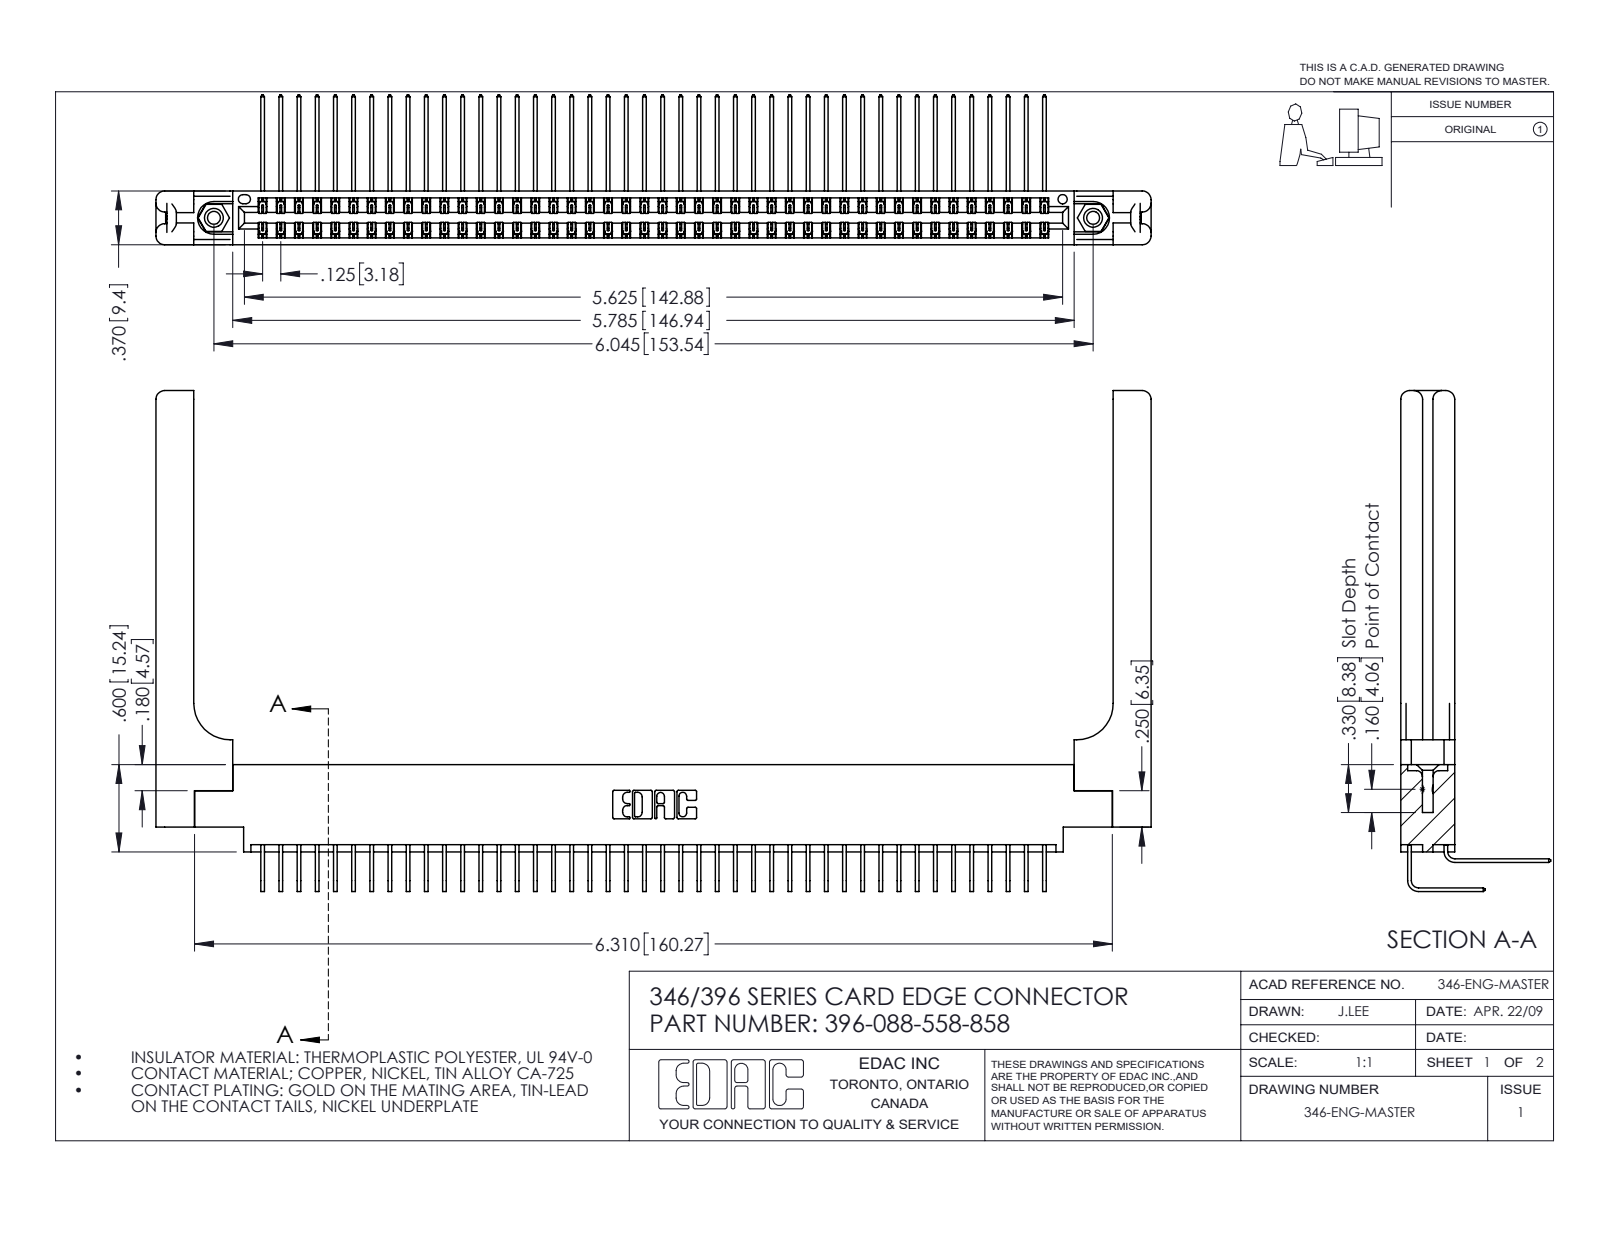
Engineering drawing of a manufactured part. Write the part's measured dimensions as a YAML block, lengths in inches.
part_name: "396-088-558-858; 345-292-001_558 Tail - 2; 346 Part_0.170 Offset - 0.156 Dia-TH; 346-220-058_345-220-058 (+2 more)"
step_written_by: "SolidWorks 2016 (CONFIG_CONTROL_DESIGN)"
units: inches
bodies: {solids: 93, faces: 5134, planar: 3484, cylindrical: 1590, other: 60}
overall_size: [6.841, 3.443, 1.03]
volume: 1.514
surface_area: 48.7
round_holes:
  - {diameter: 0.089, count: 2}
  - {diameter: 0.125, count: 2}
  - {diameter: 0.156, count: 2}
  - {diameter: 0.064, count: 1}
round_bosses_or_shafts:
  - {diameter: 0.155, count: 2}
partial_cylinders:
  - {radius: 0.006, count: 132}
  - {radius: 0.01, count: 22}
  - {radius: 0.06, count: 16}
  - {radius: 0.007, count: 6}
  - {radius: 0.031, count: 6}
  - {radius: 0.026, count: 3}
  - {radius: 0.014, count: 2}
  - {radius: 0.022, count: 2}
face_to_face_distances: [0.322, 0.048, 0.37, 0.072, 0.025, 0.298, 0.148, 0.15, 0.25, 0.275]
hole_center_spacings: [0.246, 5.836, 6.045]
